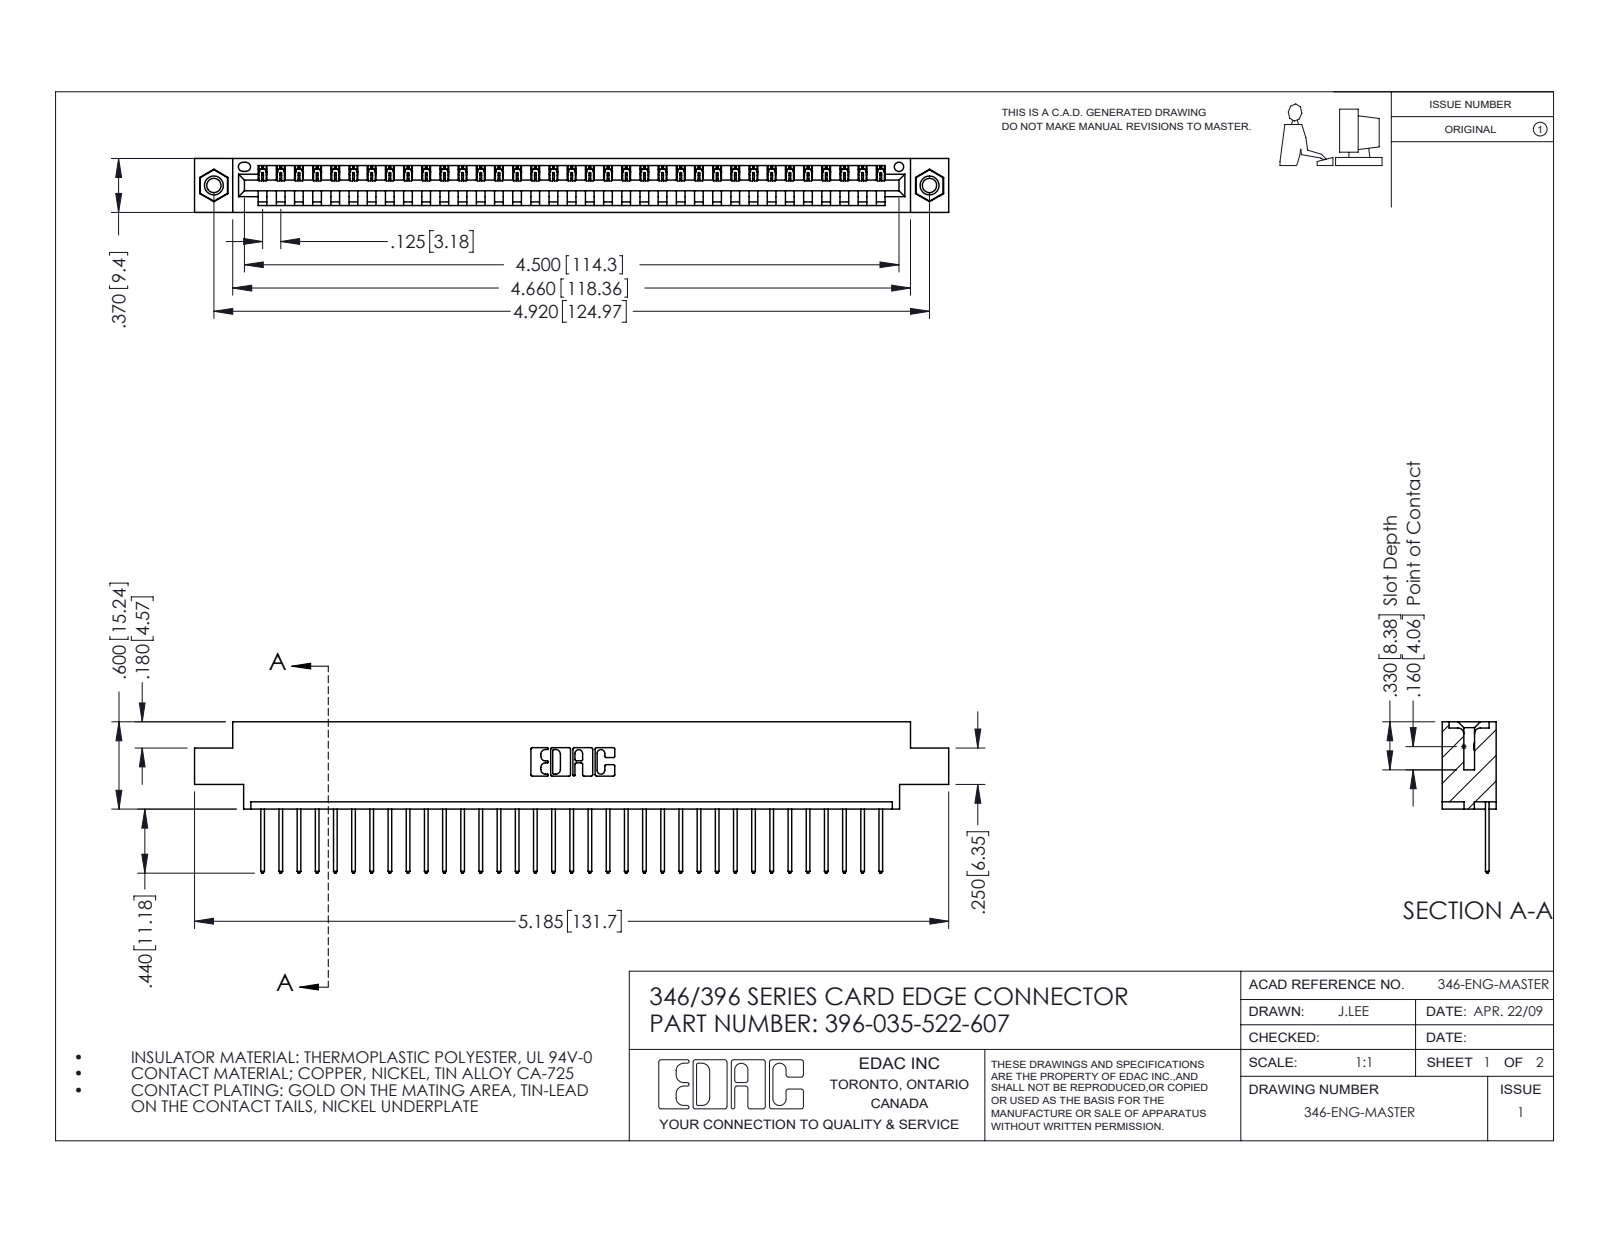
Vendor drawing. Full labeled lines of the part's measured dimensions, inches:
Part name (STEP PRODUCT): 396-035-522-607; 346 Part_0.170 Offset - 0.156 Dia-TI; 345-292-001_345-293-122; 345-250-001_345-250-005-103
STEP written by: SolidWorks 2016 (CONFIG_CONTROL_DESIGN)
Units: inches
Bodies: 38 solids, 2216 faces (1512 planar, 688 cylindrical, 16 other)
Overall size (bounding box): 5.185 × 1.04 × 0.37
Volume: 0.756 in³ · Surface area: 24.4 in²
Round holes (diameter × count): ⌀0.098 ×2, ⌀0.125 ×2, ⌀0.156 ×2, ⌀0.064 ×1
Round bosses / shafts (diameter × count): ⌀0.155 ×2
Partial cylindrical surfaces — rounded edges, fillets, slot ends (radius × count): R0.006 ×70, R0.01 ×70, R0.01 ×22, R0.007 ×6, R0.031 ×6, R0.026 ×3, R0.031 ×2, R0.04 ×2
Main face-to-face distances: 0.048, 0.322, 0.37, 0.25, 0.072, 0.298, 0.025, 0.222, 0.148, 0.1
Hole centre spacings: 0.246, 4.711, 4.92
